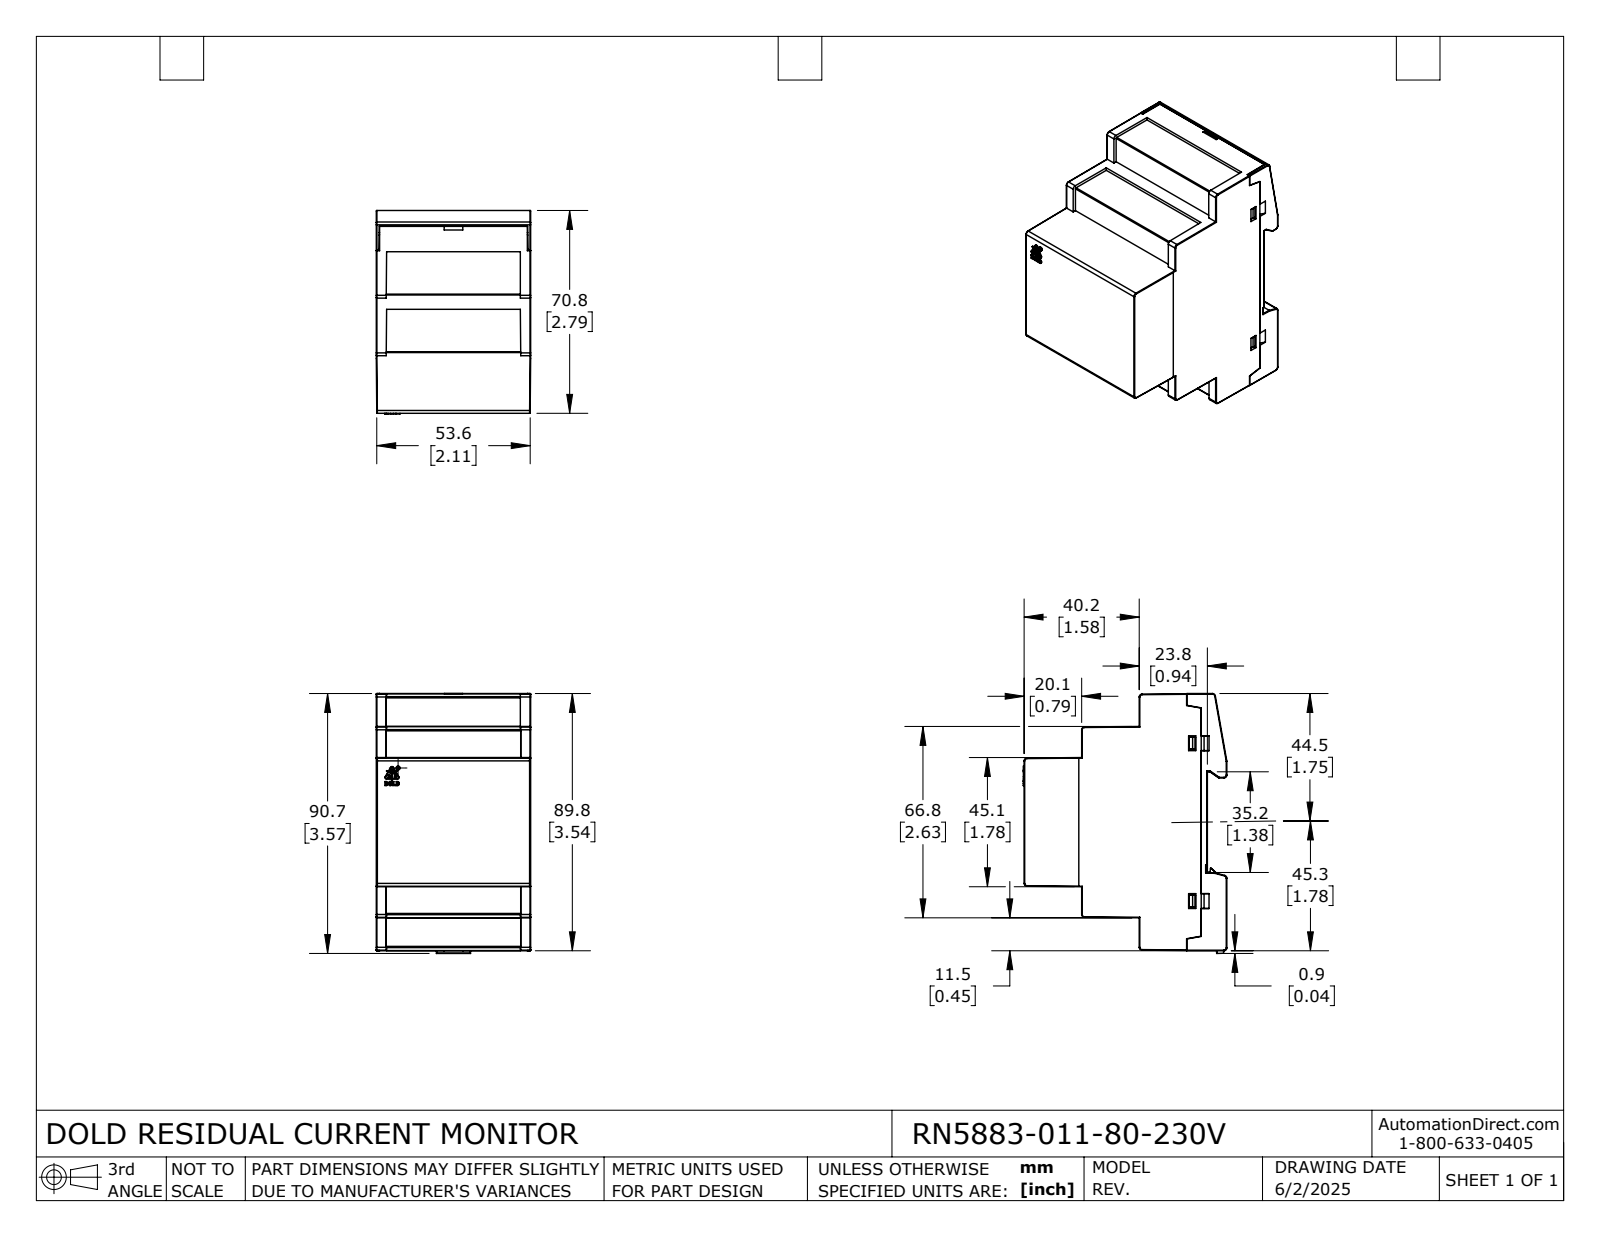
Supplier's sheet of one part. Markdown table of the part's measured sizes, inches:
| quantity | value |
| --- | --- |
| part name | RN5883-011-80-230V |
| STEP written by | SolidWorks 2024 (AUTOMOTIVE_DESIGN) |
| units | inches |
| bodies | 13 solids, 1307 faces (1035 planar, 186 cylindrical, 86 other) |
| overall size | 3.572 × 2.797 × 2.122 |
| volume | 14.21 in³ |
| surface area | 80.85 in² |
| round holes (diameter × count) | 0.049 × 1 |
| round bosses / shafts (diameter × count) | 0.098 × 6, 0.157 × 4, 0.181 × 1, 0.053 × 1 |
| partial cylindrical surfaces (radius × count) | 0.008 × 44, 0.004 × 19, 0.039 × 18, 0.02 × 11, 0.005 × 6, 0.004 × 4, 0.012 × 4, 0.021 × 3 |
| main face-to-face distances | 0.136, 2.122, 1.986, 0.063, 0.073, 2.049, 1.913, 0.041, 2.435, 0.085 |
